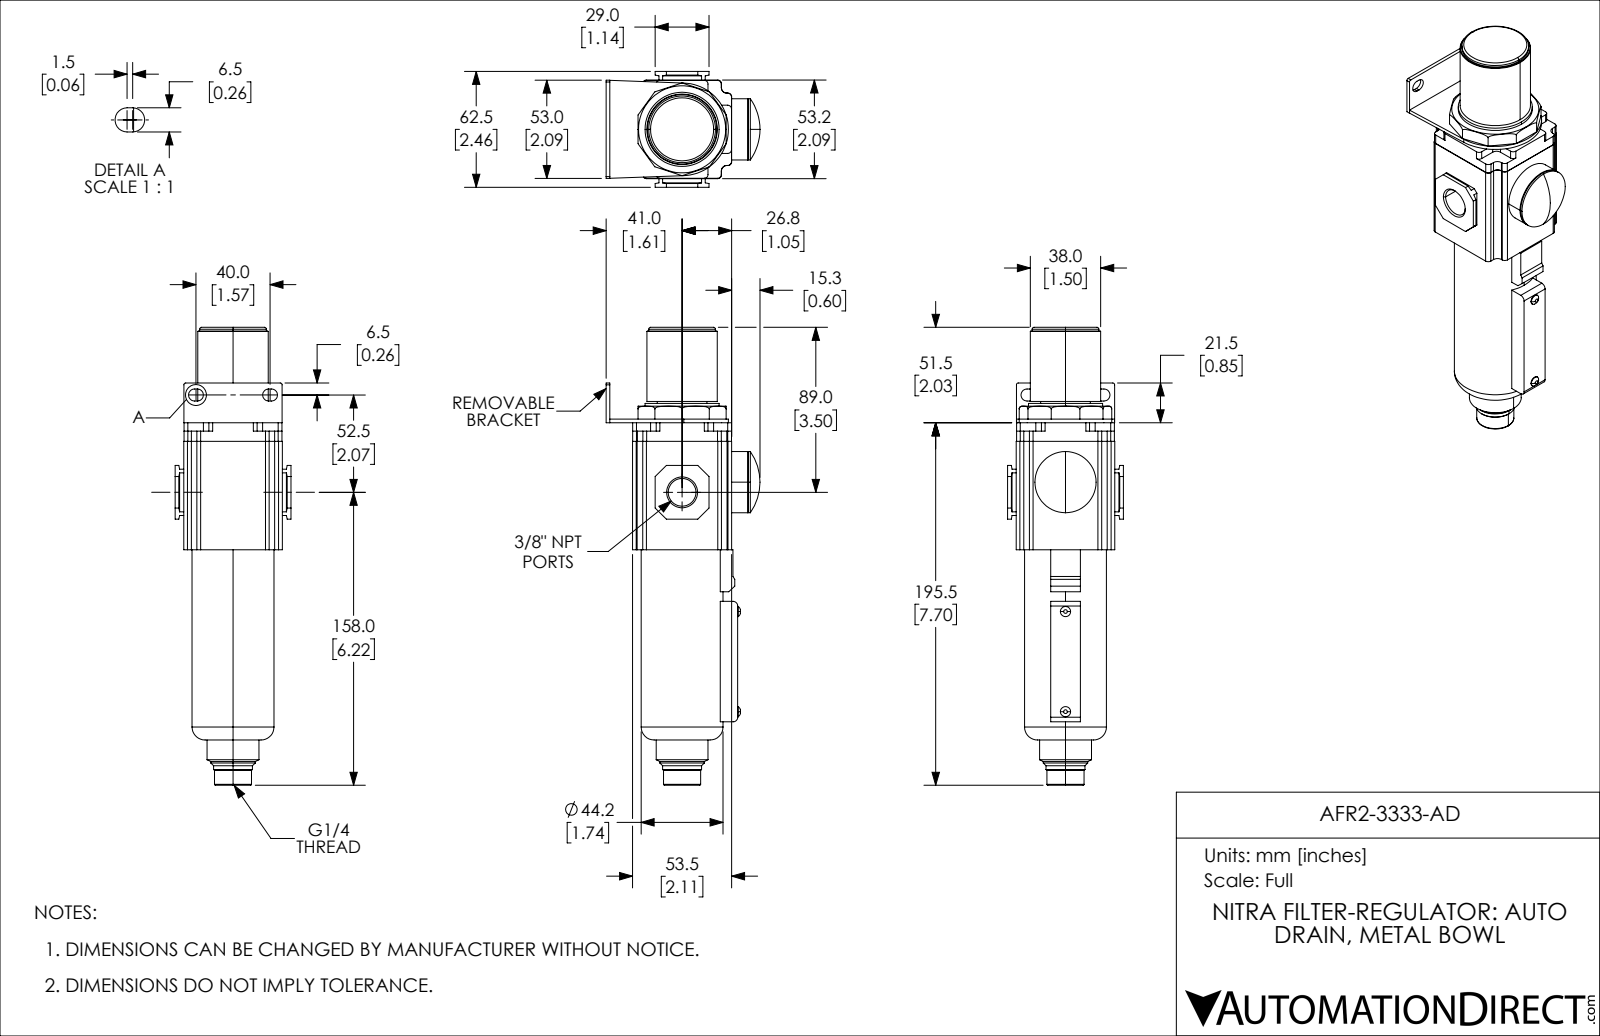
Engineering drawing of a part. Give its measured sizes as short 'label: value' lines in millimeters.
name: AFR2-3333-AD
written by: SolidWorks 2019 (CONFIG_CONTROL_DESIGN)
unit: mm
bodies: 1 solid, 235 faces (128 planar, 77 cylindrical, 30 other)
size: 247 × 83.03 × 62.5
volume: 438 897 mm³; area: 52 897 mm²
holes: 1× ⌀11.45, 1× ⌀14.95
bosses: 2× ⌀5.5, 1× ⌀44.2, 1× ⌀40, 1× ⌀38, 1× ⌀36, 1× ⌀33, 1× ⌀28, 1× ⌀26.78
rounds: 24× R2, 12× R3, 4× R3.25, 2× R1, 2× R2.5, 1× R25
face distances: 2, 53.2, 18.6, 34.6, 16, 53.5, 39.25, 14.25, 4.65, 23.25
